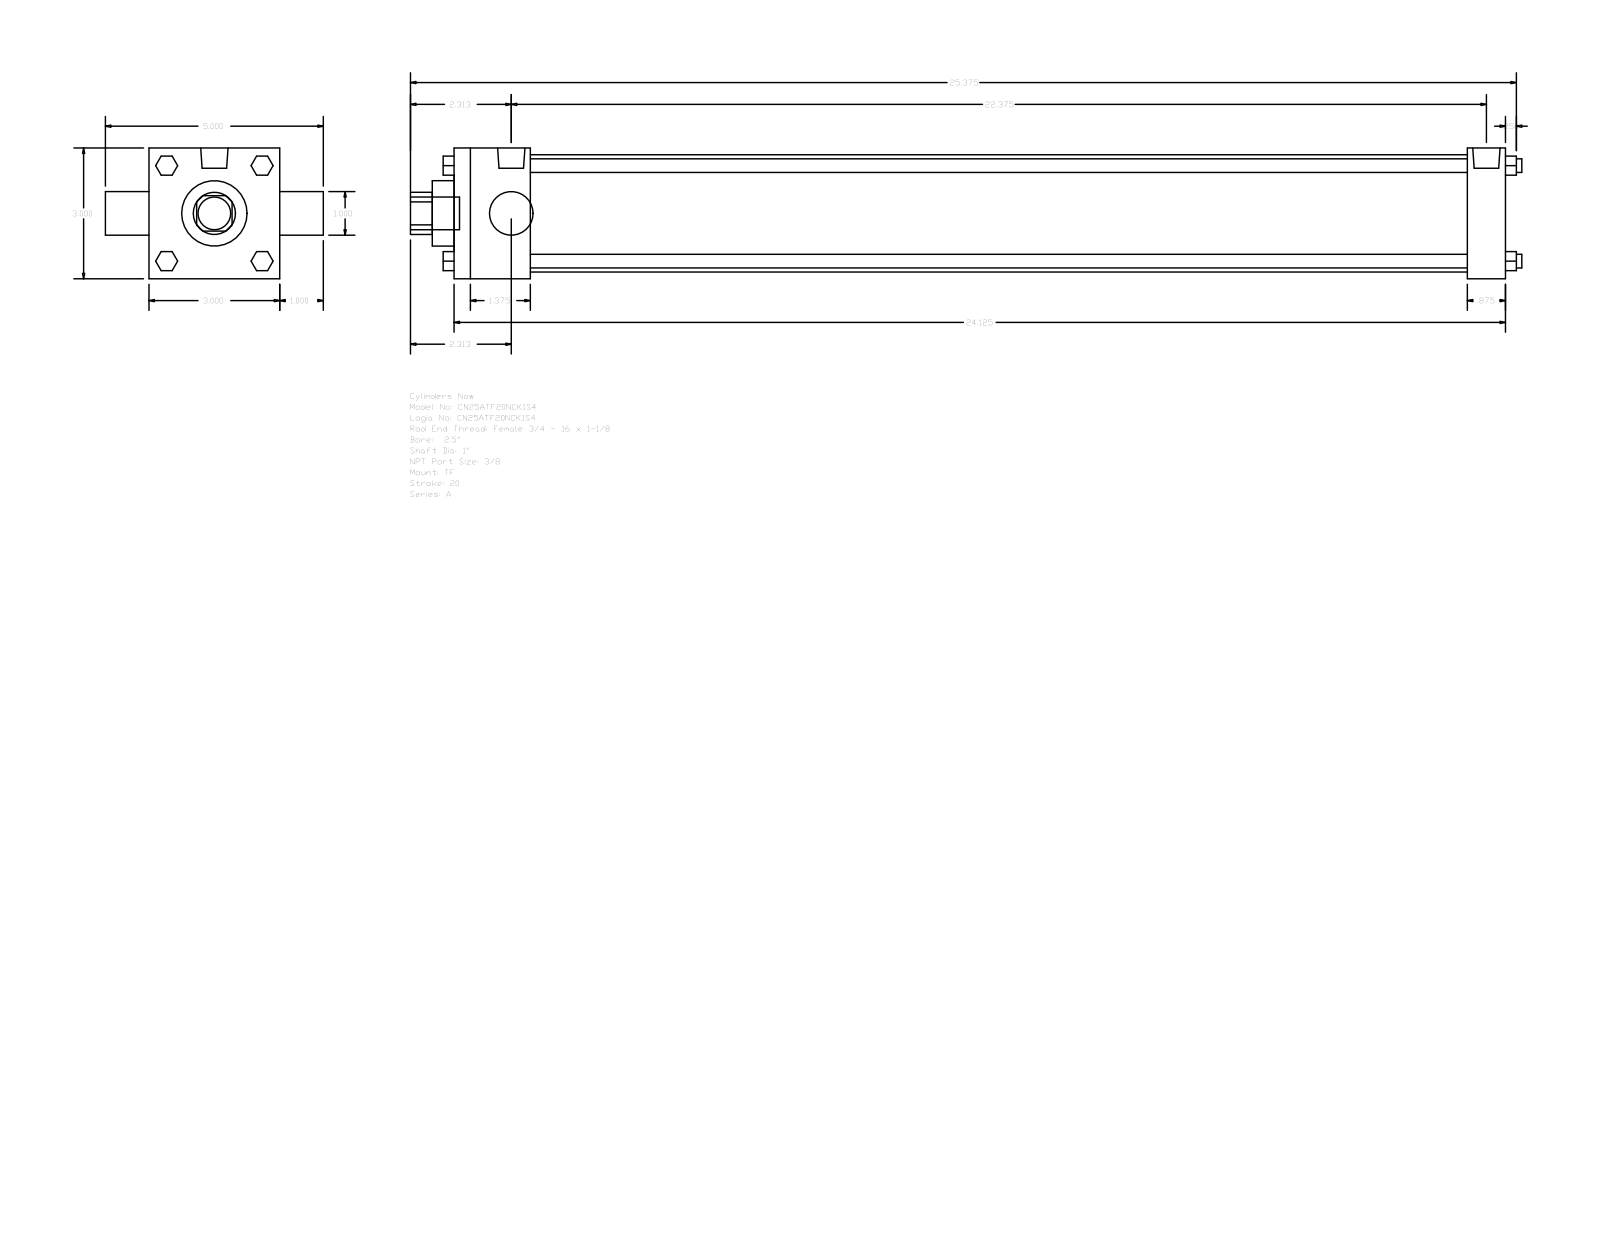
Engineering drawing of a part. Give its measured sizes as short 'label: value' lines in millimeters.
name: A_TF__0250_1
written by: GSSL Pune (CONFIG_CONTROL_DESIGN)
unit: mm
bodies: 0 solids, 120 faces (92 planar, 28 cylindrical, 0 other)
size: 647.7 × 127 × 76.2
holes: 2× ⌀25.4, 1× ⌀38.1, 1× ⌀68.33
bosses: 4× ⌀7.94, 3× ⌀5.56, 2× ⌀15.93, 1× ⌀19.05
rounds: 1× R12.29
face distances: 76.2, 612.77, 44.45, 590.55, 546.1, 568.32, 22.22, 25.4, 101.6, 625.47
